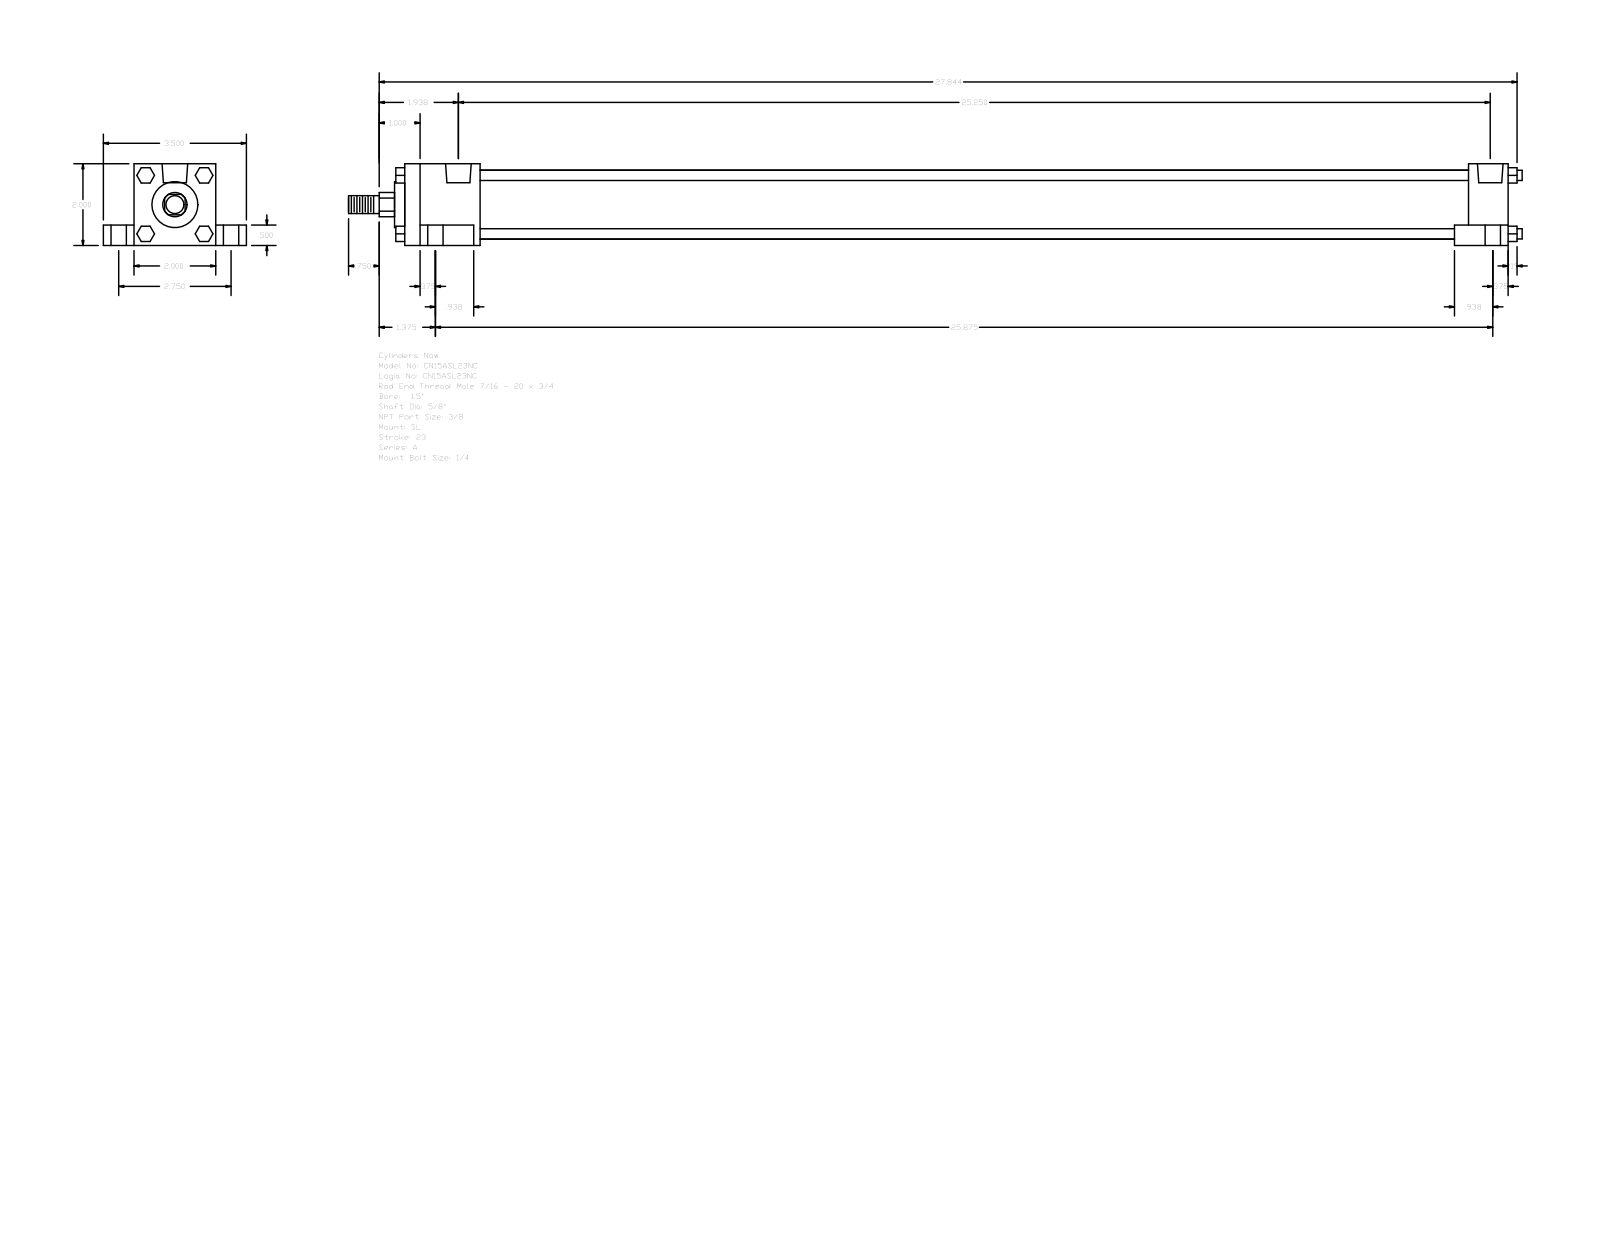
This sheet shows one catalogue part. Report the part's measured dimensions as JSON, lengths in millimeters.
{"part_name": "A_SL__0150_0.625", "step_written_by": "GSSL Pune (CONFIG_CONTROL_DESIGN)", "units": "millimeters", "bodies": {"solids": 0, "faces": 148, "planar": 112, "cylindrical": 36, "other": 0}, "overall_size": [729.46, 88.9, 50.8], "round_holes": [[5.56, 4], [9.53, 4], [15.88, 4], [15.93, 2]], "round_bosses_or_shafts": [[6.35, 4], [42.93, 1], [28.57, 1], [15.88, 1], [11.11, 1]], "partial_cylinders_radius": [[7.54, 1]], "face_to_face_distances": [50.8, 19.05, 38.1, 12.7, 69.85, 685.79, 9.52, 661.19, 24.6, 46.83], "hole_center_spacings": [3.97, 34.96, 35.36, 37.73, 39.41, 69.84, 633.41, 637.38]}
